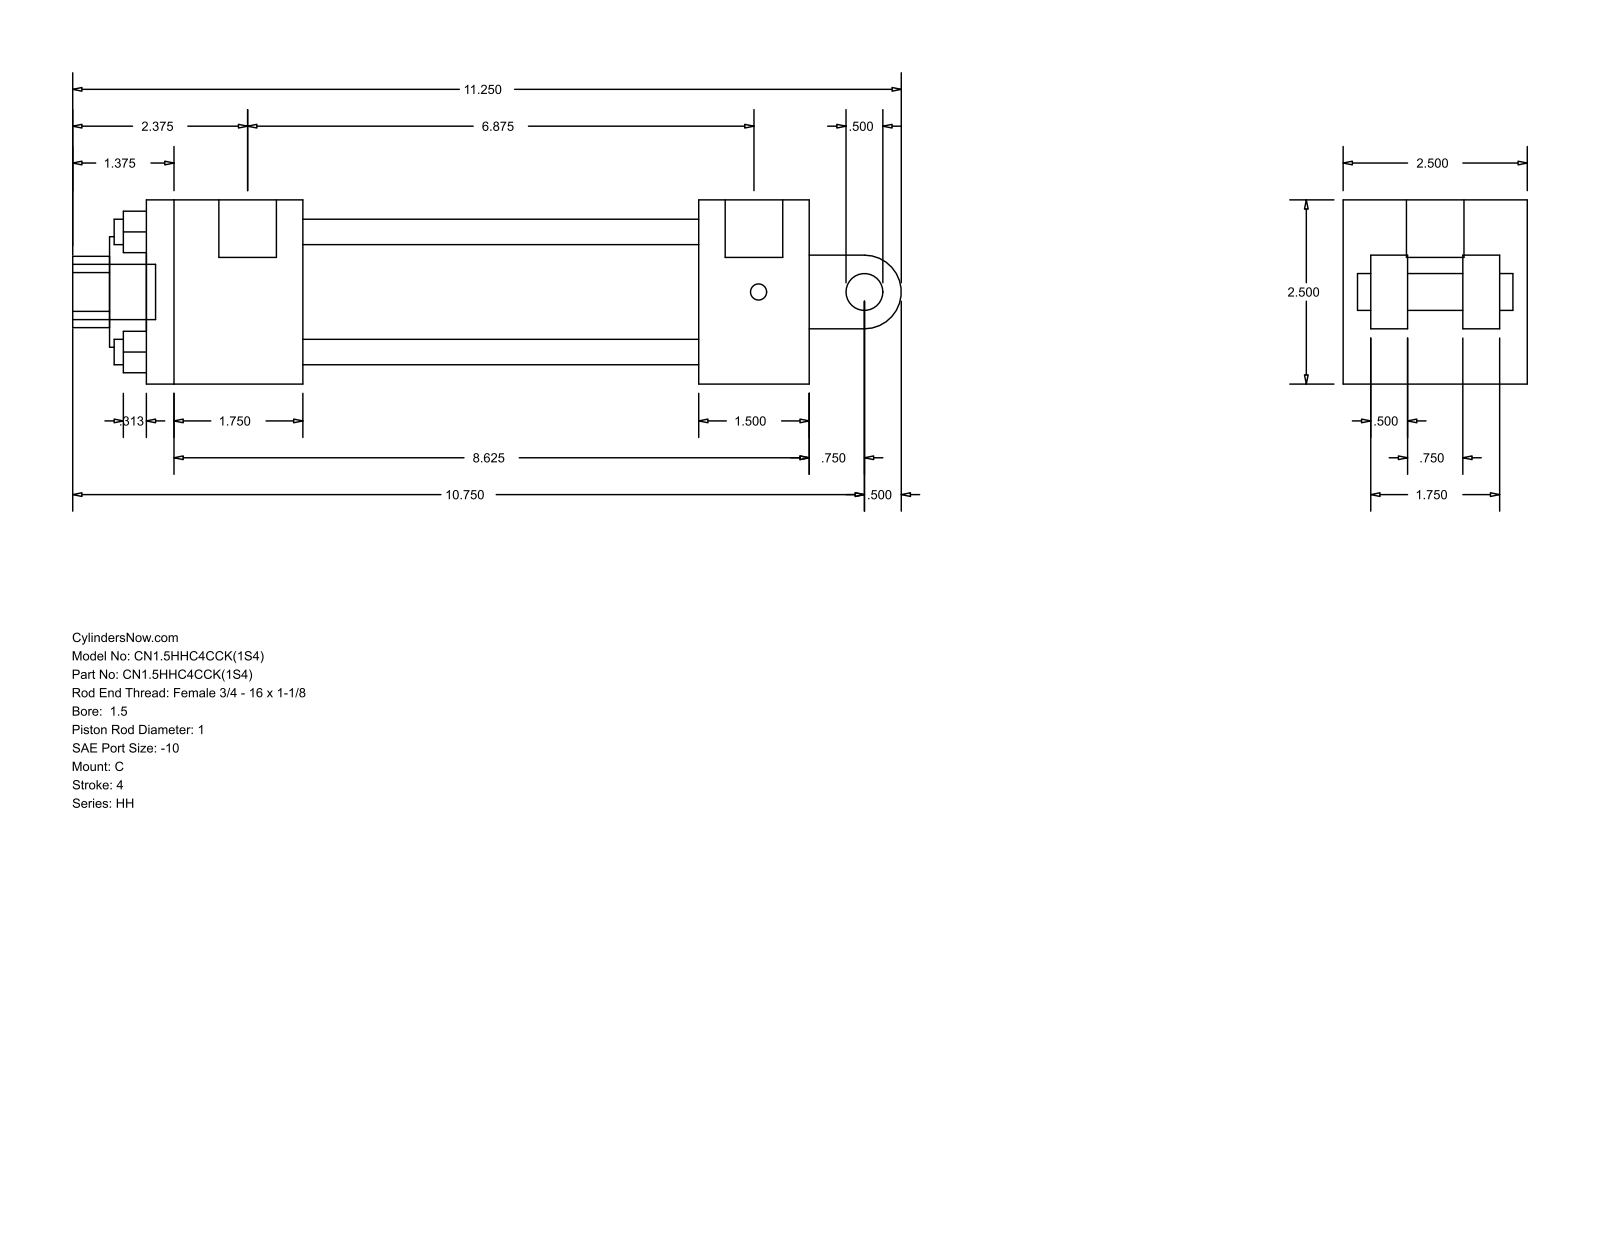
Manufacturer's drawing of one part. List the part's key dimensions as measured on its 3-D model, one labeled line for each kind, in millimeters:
Part name (STEP PRODUCT): HH_C__0150_1
STEP written by: GSSL Pune (CONFIG_CONTROL_DESIGN)
Units: millimetres
Bodies: 0 solids, 99 faces (70 planar, 29 cylindrical, 0 other)
Overall size (bounding box): 285.75 × 63.5 × 63.5
Round holes (diameter × count): ⌀8.76 ×4, ⌀5.56 ×2, ⌀19.84 ×1, ⌀25.4 ×1, ⌀38.1 ×1, ⌀44.45 ×1
Round bosses / shafts (diameter × count): ⌀5.56 ×2, ⌀19.84 ×1, ⌀19.05 ×1, ⌀12.7 ×1
Partial cylindrical surfaces — rounded edges, fillets, slot ends (radius × count): R12.29 ×1, R12.7 ×1
Main face-to-face distances: 63.5, 53.98, 136.52, 174.62, 38.1, 190.5, 228.6, 12.7, 22.22, 41.28
Hole centre spacings: 29.27, 41.4, 58.55, 1.59
